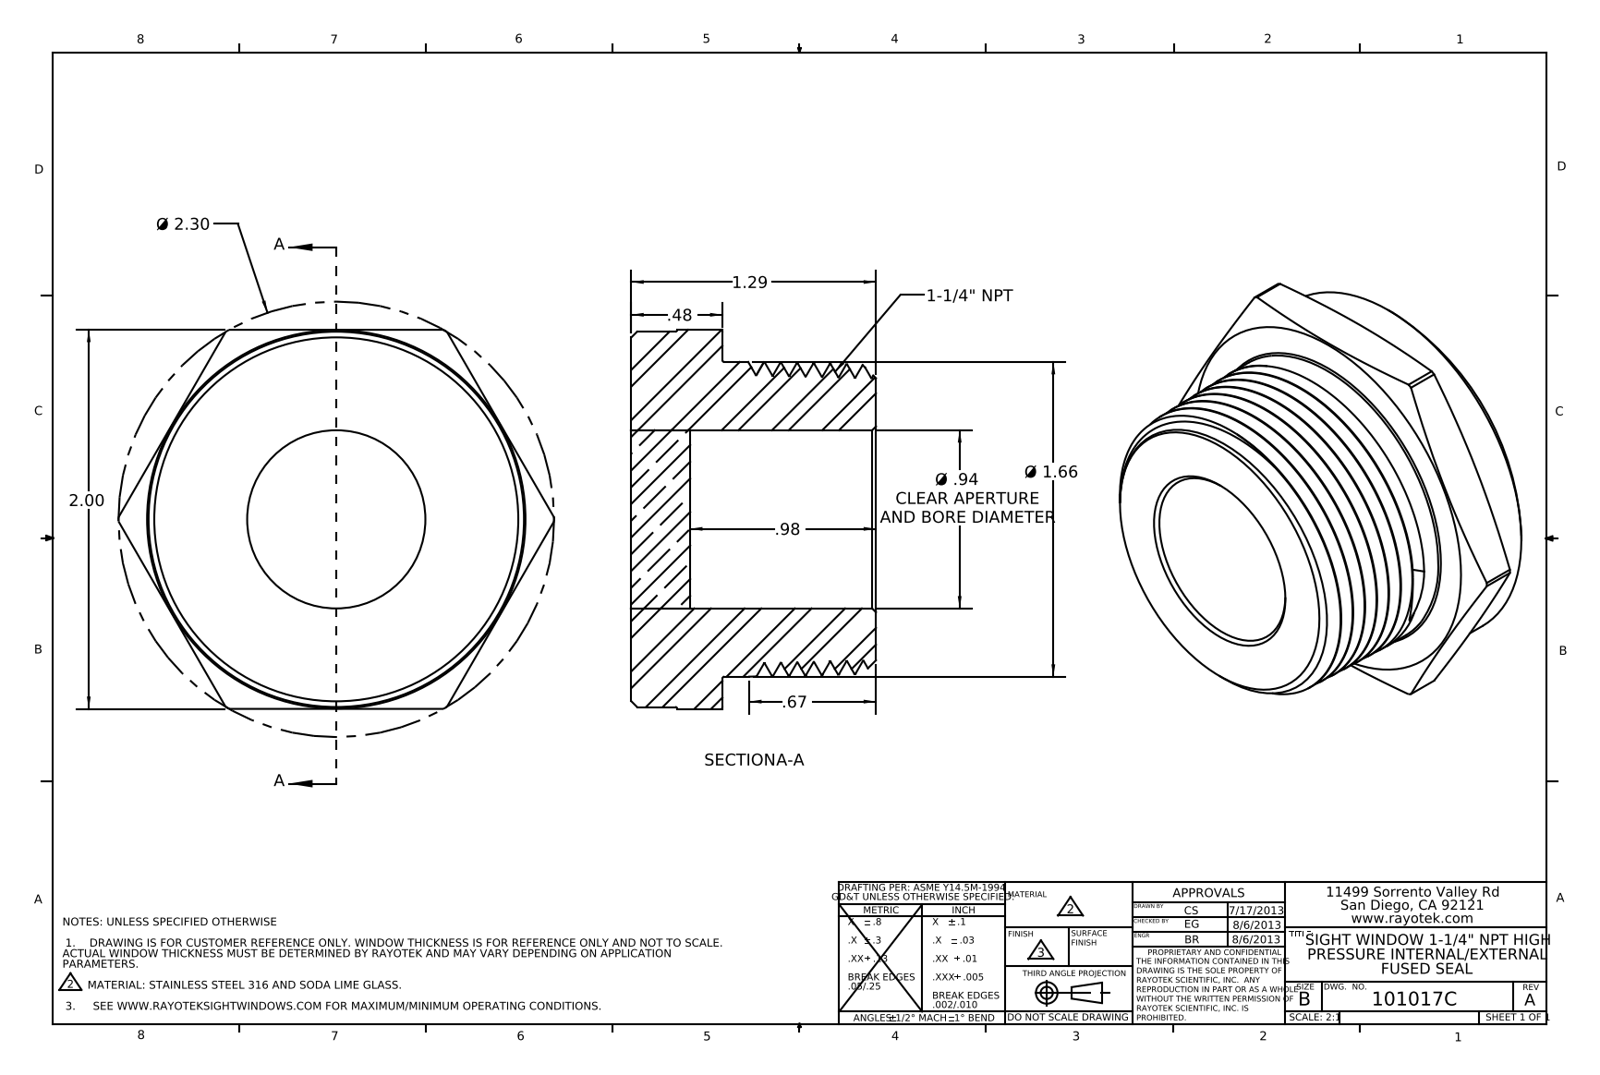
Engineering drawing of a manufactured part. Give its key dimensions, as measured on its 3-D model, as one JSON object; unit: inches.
{"part_name": "101017; 402017; 403017_CUSTOMER", "step_written_by": "SolidWorks 2012 (AUTOMOTIVE_DESIGN)", "units": "inches", "bodies": {"solids": 2, "faces": 62, "planar": 14, "cylindrical": 15, "other": 33}, "overall_size": [2.297, 2, 1.29], "volume_in3": 2.488, "surface_area_in2": 20.93, "round_holes": [[0.94, 1]], "round_bosses_or_shafts": [[1.98, 1], [1.66, 1]], "partial_cylinders_radius": [[1.149, 1]], "face_to_face_distances": [1.29, 0.48, 0.81, 0.31, 0.17, 0.98, 2, 2]}
